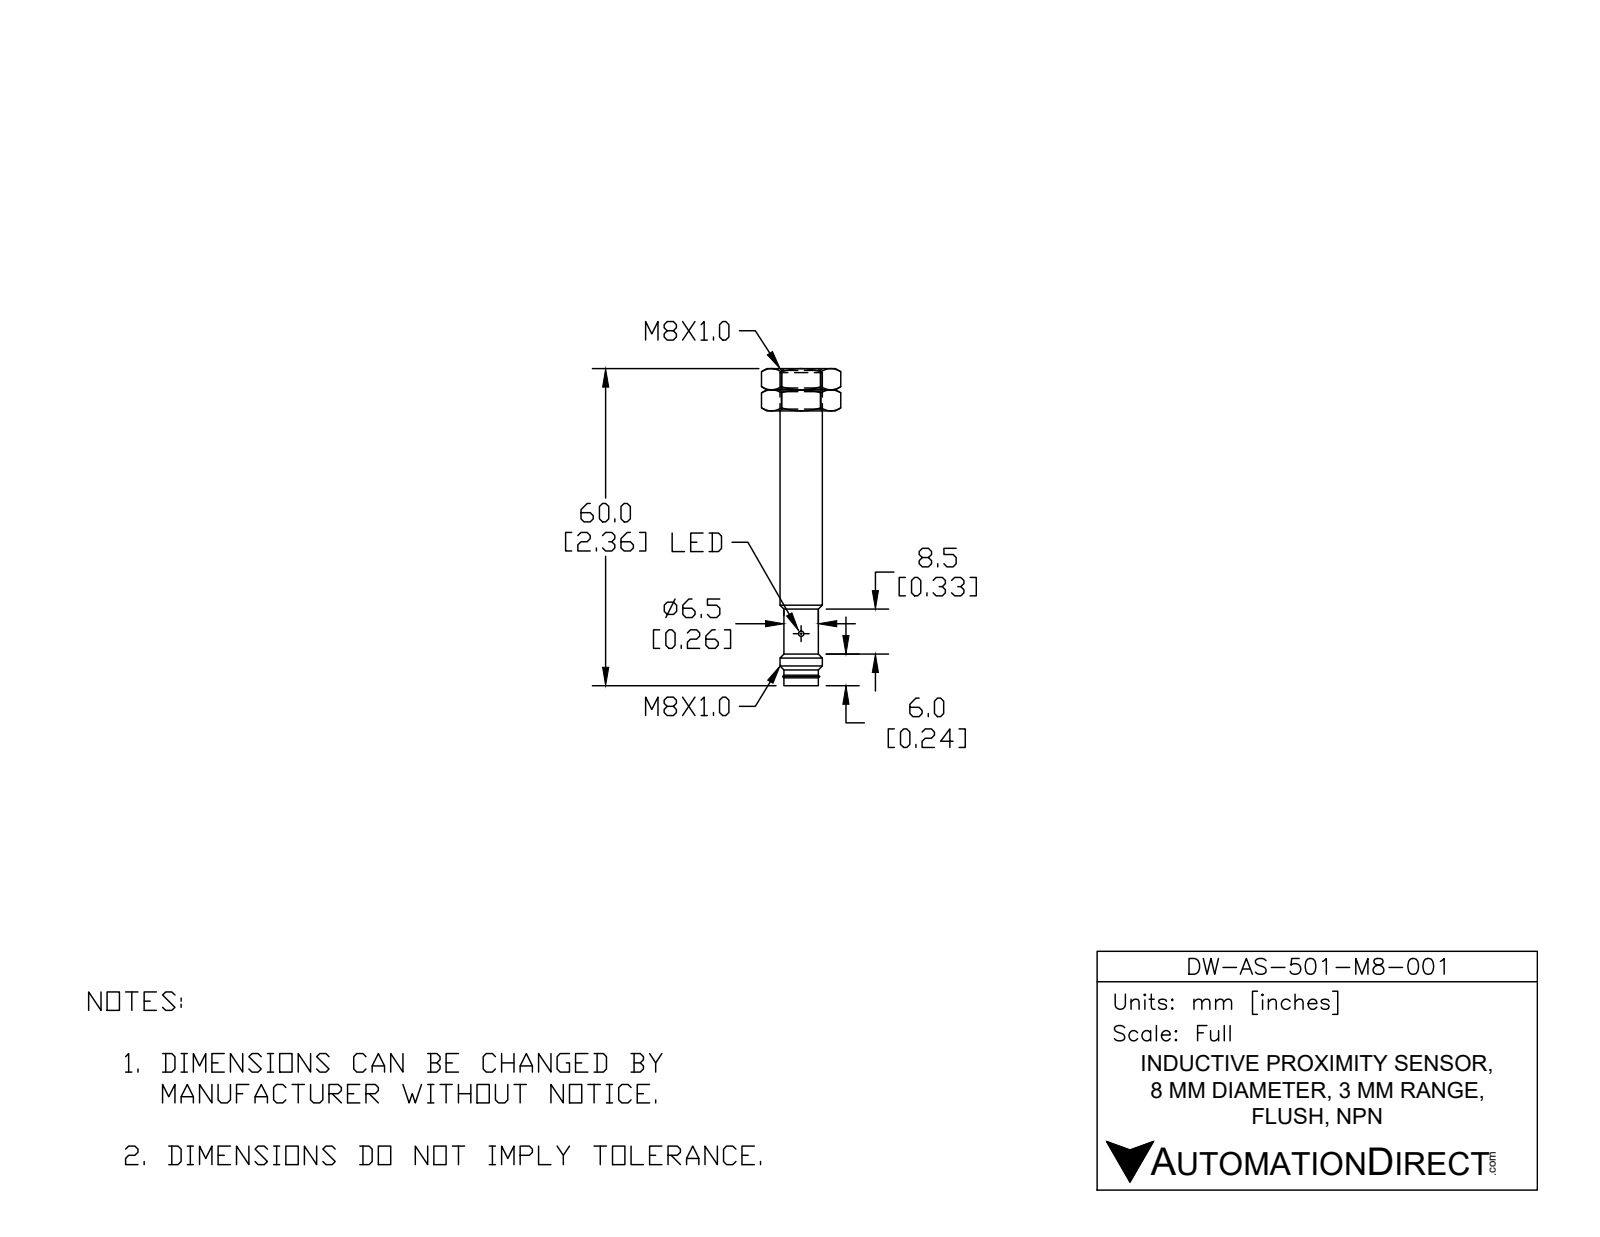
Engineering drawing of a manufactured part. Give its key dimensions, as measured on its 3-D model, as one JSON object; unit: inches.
{"part_name": "DW-AS-501-M8-001", "step_written_by": "SolidWorks 2017 (AUTOMOTIVE_DESIGN)", "units": "inches", "bodies": {"solids": 1, "faces": 36, "planar": 7, "cylindrical": 17, "other": 12}, "overall_size": [2.362, 0.315, 0.315], "volume_in3": 0.163, "surface_area_in2": 2.629, "round_holes": [[0.071, 2]], "round_bosses_or_shafts": [[0.039, 3], [0.315, 1], [0.272, 1], [0.256, 1], [0.236, 1]], "face_to_face_distances": [2.161, 2.165, 2.362, 2.358, 0.197, 2.323, 2.319, 0.157, 0.039]}
